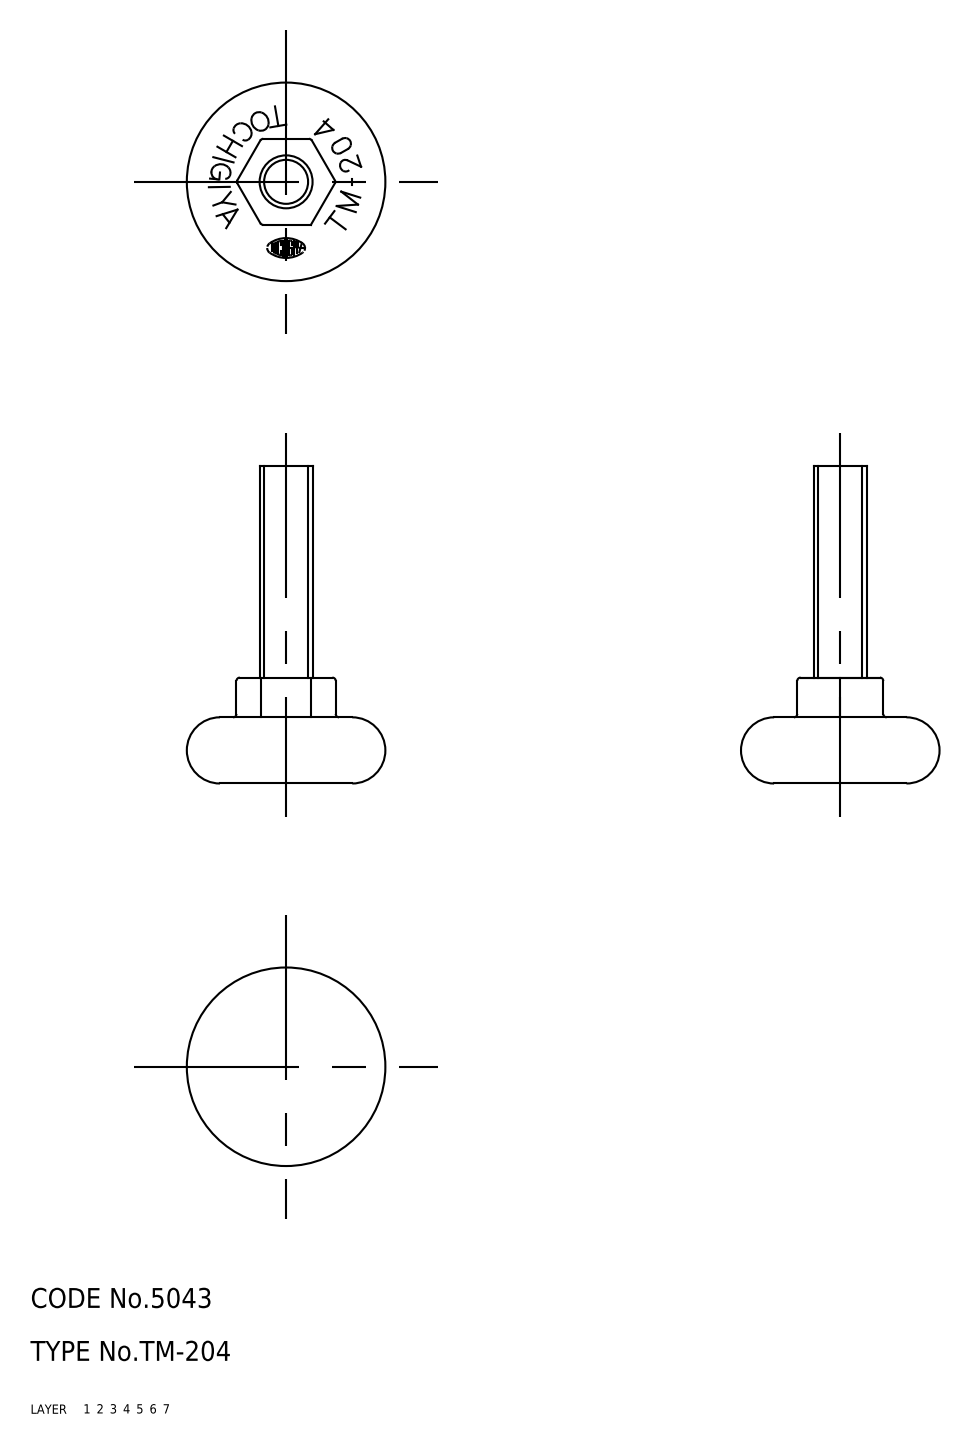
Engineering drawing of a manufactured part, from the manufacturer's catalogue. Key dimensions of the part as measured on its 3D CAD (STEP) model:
Part name (STEP PRODUCT): foot; bolt; TM_204_753_36
STEP written by: CADfix (AUTOMOTIVE_DESIGN)
Units: millimetres
Bodies: 2 solids, 52 faces (0 planar, 0 cylindrical, 52 other)
Overall size (bounding box): 48 × 30 × 30
Volume: 8 638 mm³ · Surface area: 4 278 mm²
